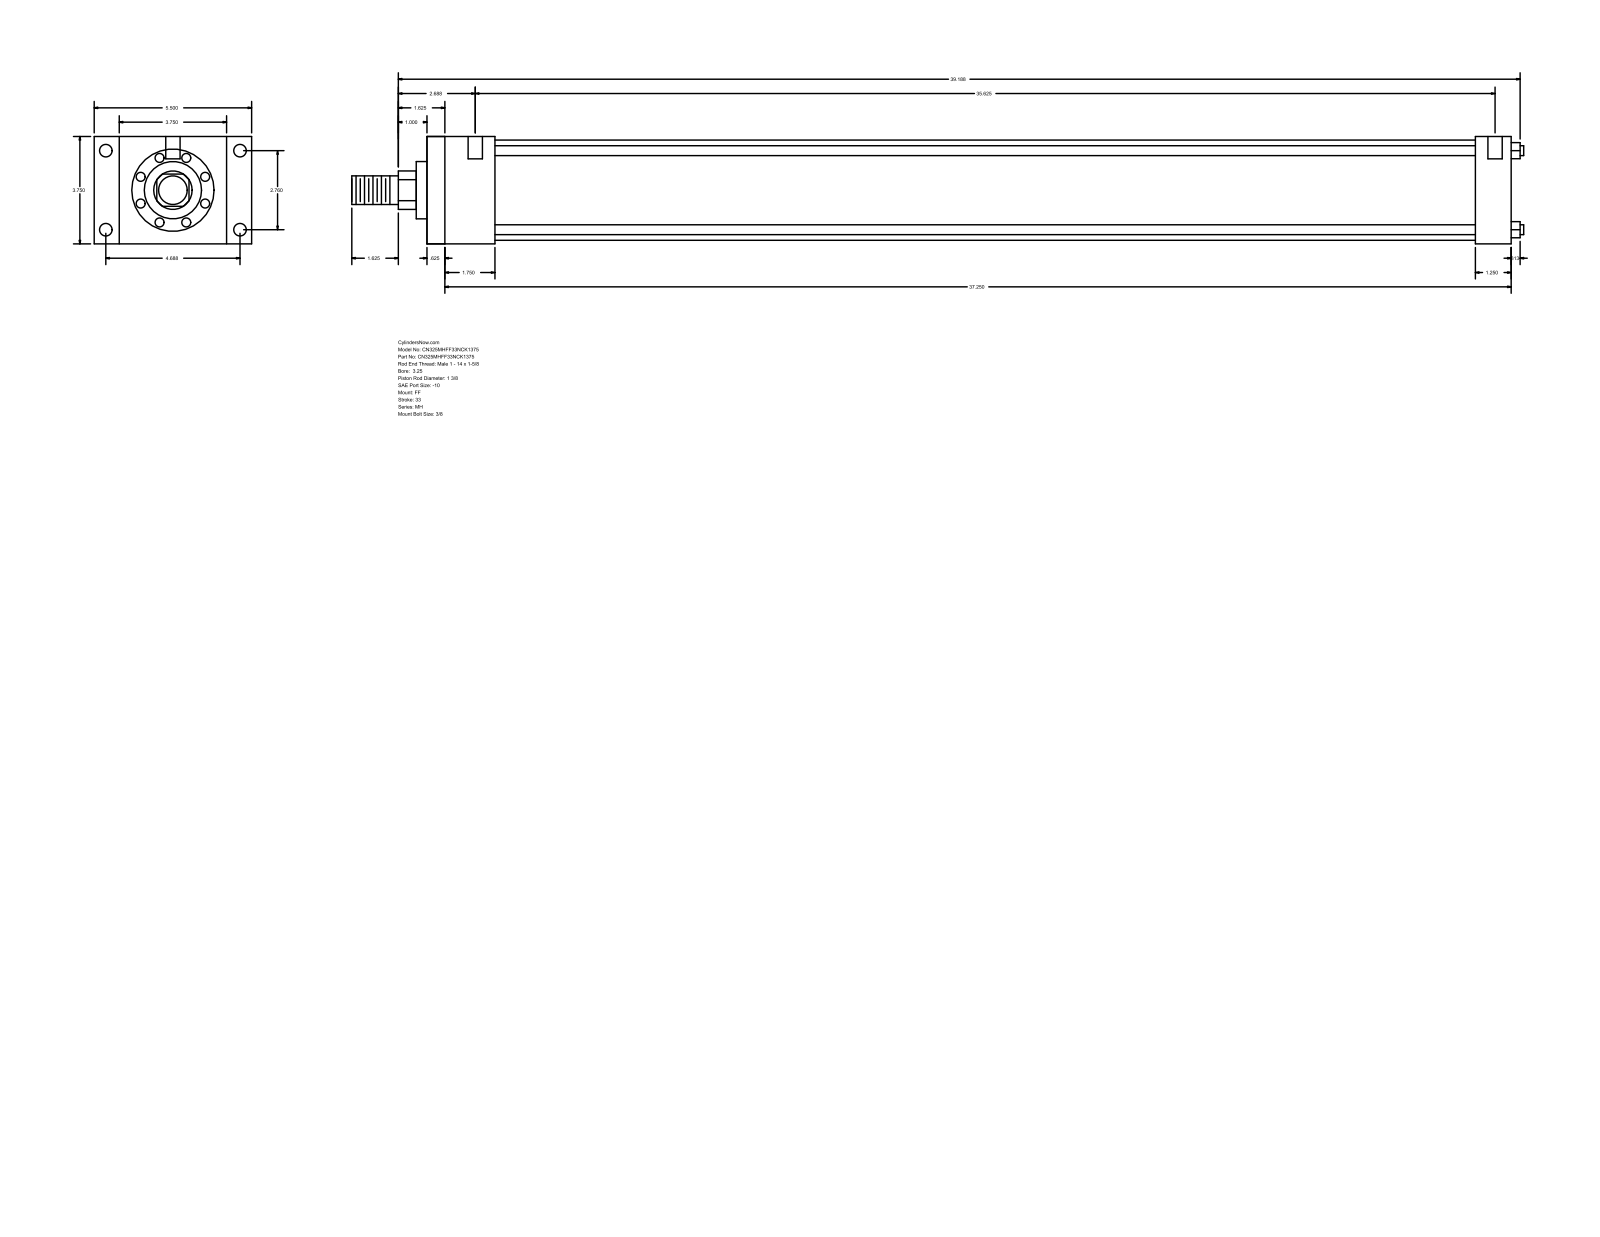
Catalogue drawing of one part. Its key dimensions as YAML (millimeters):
part_name: "MH_FF__0325_1.375"
step_written_by: "GSSL Pune (CONFIG_CONTROL_DESIGN)"
units: millimeters
bodies: {solids: 0, faces: 92, planar: 64, cylindrical: 28, other: 0}
overall_size: [1039.81, 139.7, 95.25]
round_holes:
  - {diameter: 5.56, count: 4}
  - {diameter: 11.13, count: 4}
  - {diameter: 12.7, count: 2}
round_bosses_or_shafts:
  - {diameter: 8.76, count: 4}
  - {diameter: 88.9, count: 1}
  - {diameter: 50.8, count: 1}
  - {diameter: 34.92, count: 1}
  - {diameter: 25.4, count: 1}
partial_cylinders:
  - {radius: 17.06, count: 1}
face_to_face_distances: [95.24, 962.02, 15.87, 946.15, 22.23, 117.47, 930.27, 914.4, 31.75, 60.32]
hole_center_spacings: [70.1, 119.06, 138.16, 911.23, 1.59, 4.76, 904.88, 906.47]
